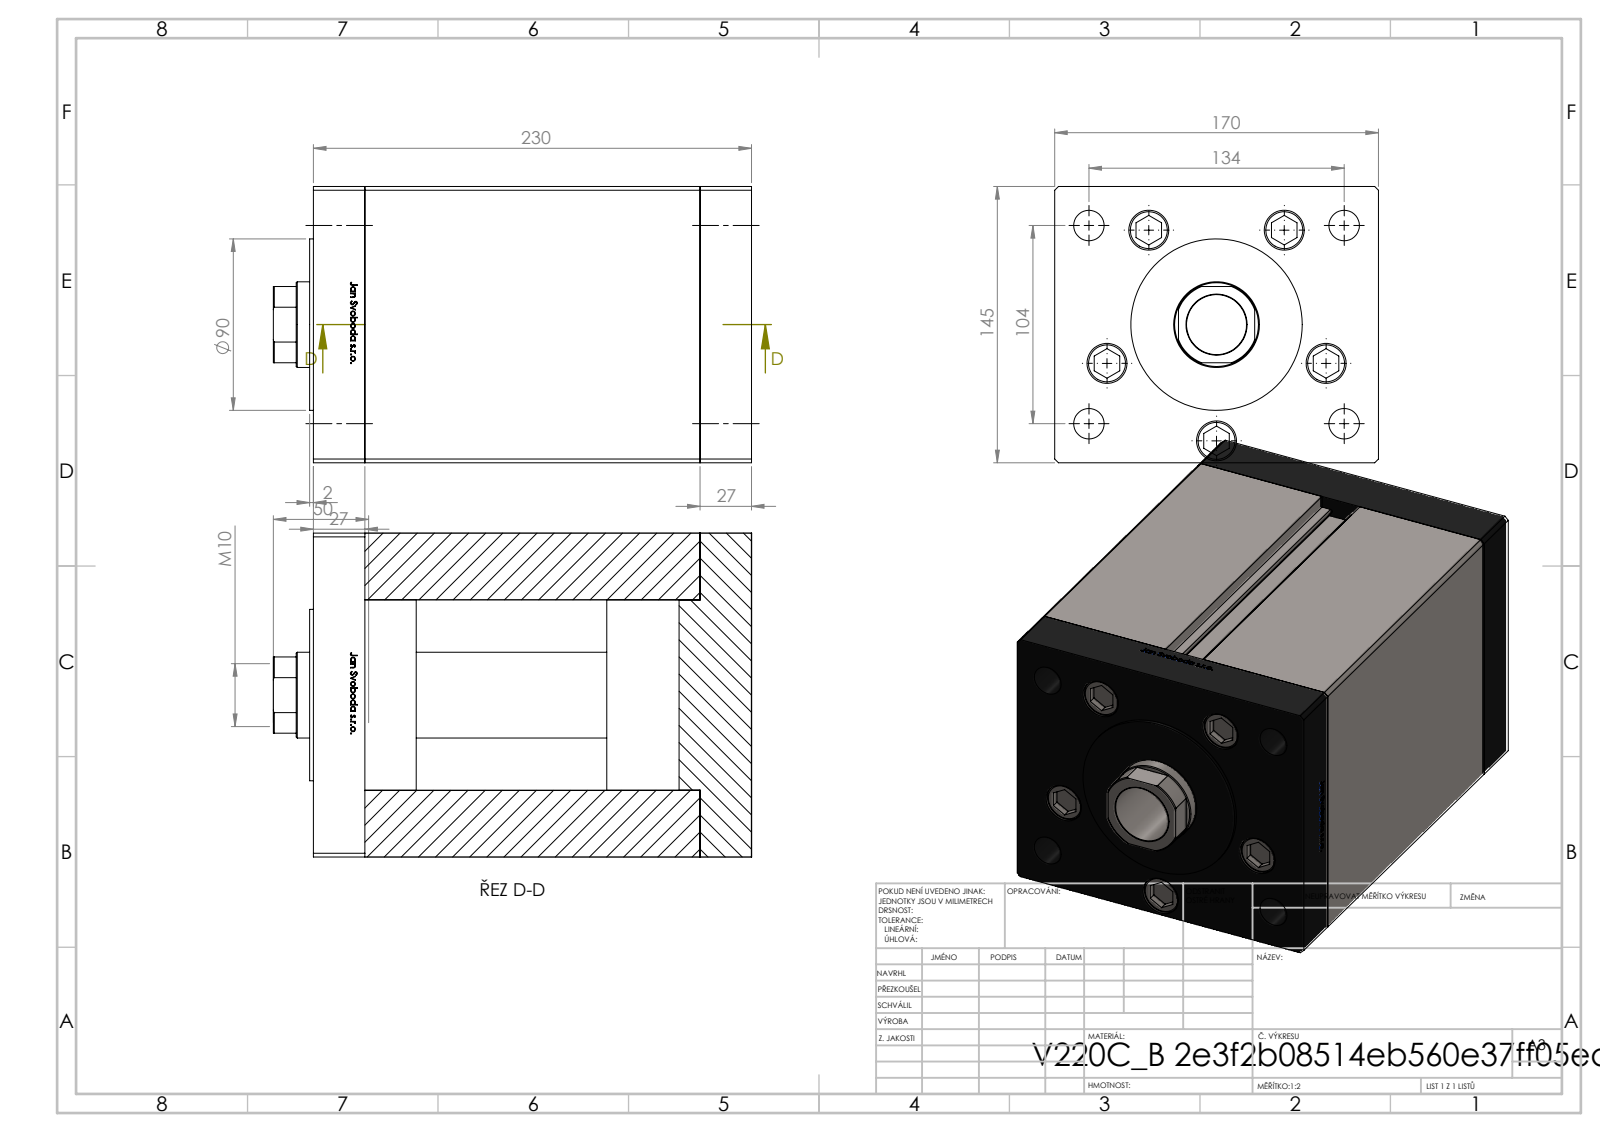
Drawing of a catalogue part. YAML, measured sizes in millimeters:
part_name: "V220C_B MIDDLE; ALLEN BOLT; V220C_VC_B; V220C BACK_B (+1 more)"
step_written_by: "SolidWorks 2019 (CONFIG_CONTROL_DESIGN)"
units: millimeters
bodies: {solids: 14, faces: 1185, planar: 464, cylindrical: 147, other: 574}
overall_size: [251, 170, 145]
volume: 4878000
surface_area: 455142
round_holes:
  - {diameter: 17.5, count: 5}
  - {diameter: 21, count: 5}
  - {diameter: 16, count: 4}
  - {diameter: 2, count: 2}
  - {diameter: 13.16, count: 2}
  - {diameter: 31.5, count: 1}
  - {diameter: 45, count: 1}
round_bosses_or_shafts:
  - {diameter: 8, count: 5}
  - {diameter: 100, count: 1}
  - {diameter: 90, count: 1}
partial_cylinders:
  - {radius: 0.93, count: 2}
  - {radius: 22, count: 1}
face_to_face_distances: [27, 203, 176, 145, 170, 38, 11, 230, 165, 192]
hole_center_spacings: [61, 84.81, 31.53, 33.06, 67.6, 70.44, 72.95, 73.26]
